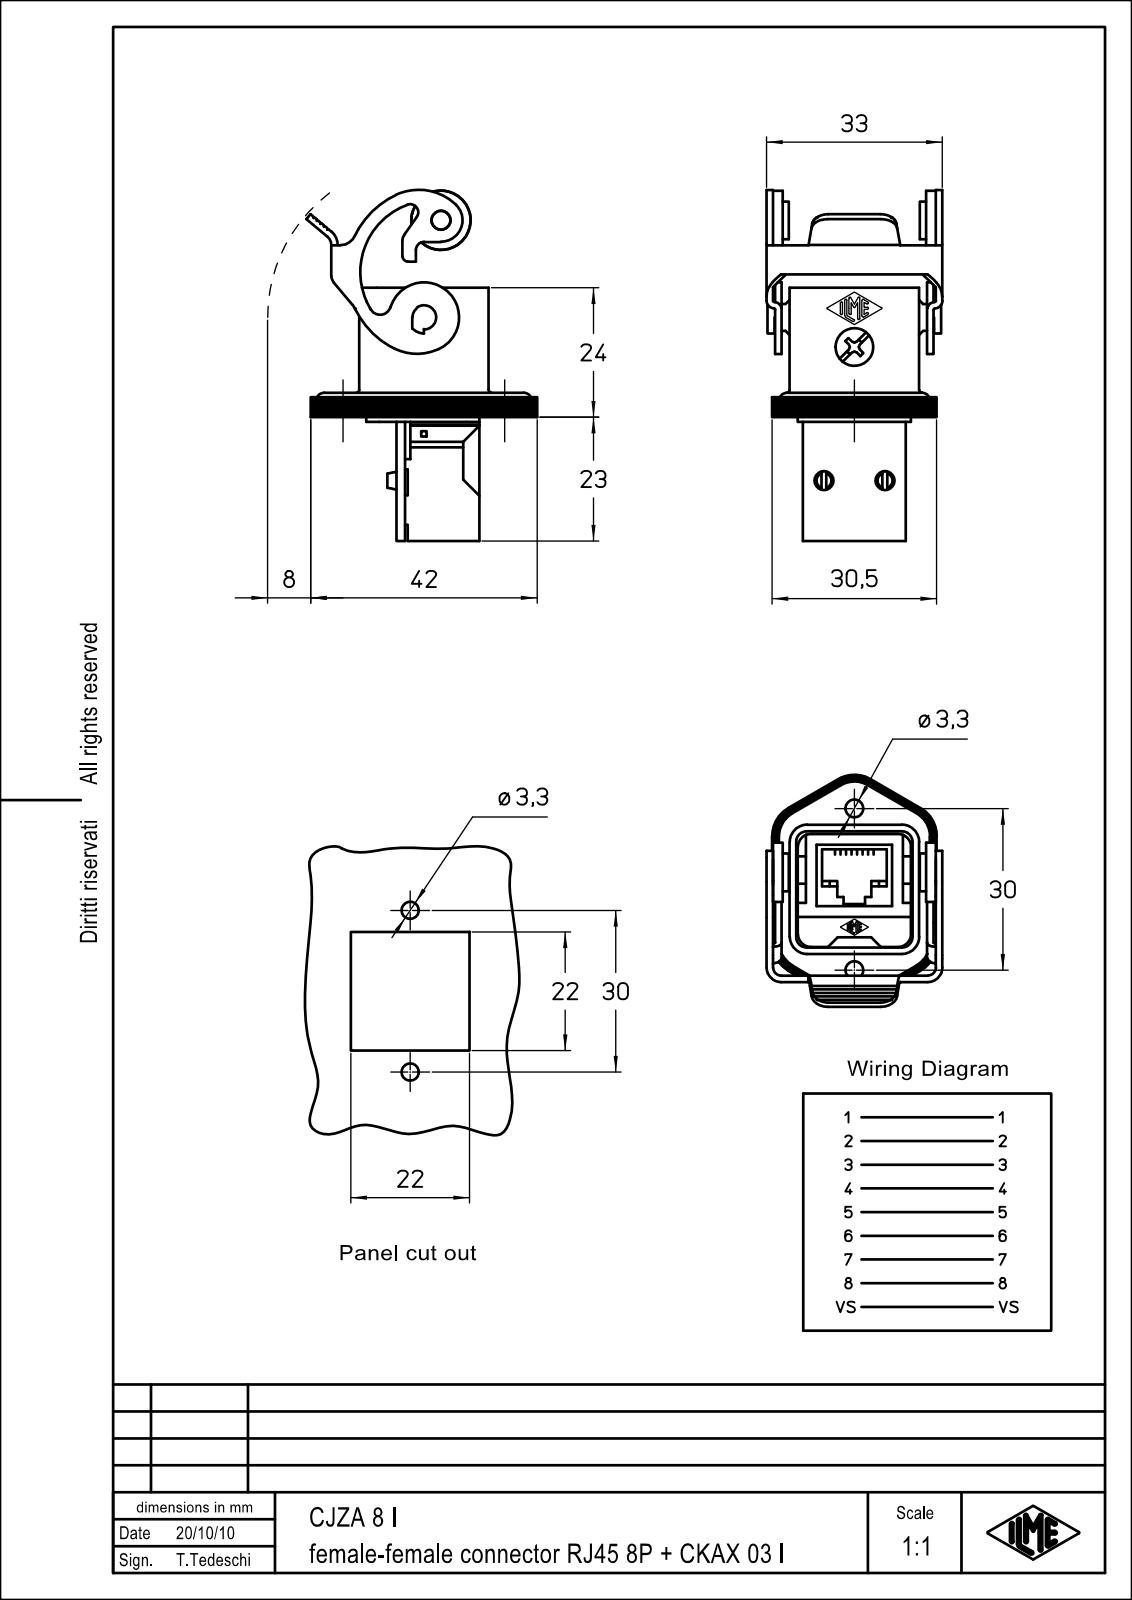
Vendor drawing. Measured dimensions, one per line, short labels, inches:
name: Cust_zama_I; CJZA_8_I
written by: Creo Elements/Direct Modeling 18.0B 02-Dec-2011 (C) Parametric Technology GmbH (AUTOMOTIVE_DESIGN)
unit: in
bodies: 1 solid, 577 faces (367 planar, 173 cylindrical, 37 other)
size: 2.573 × 1.695 × 1.299
volume: 1.081 in³; area: 23.42 in²
holes: 4× ⌀0.138, 2× ⌀0.13, 1× ⌀0.079, 1× ⌀0.197, 1× ⌀0.236
bosses: 4× ⌀0.134, 1× ⌀0.433, 1× ⌀0.276, 1× ⌀0.22, 1× ⌀0.197, 1× ⌀0.189, 1× ⌀0.169, 1× ⌀0.138
rounds: 16× R0.008, 14× R0.004, 8× R0.059, 8× R0.079, 6× R0.246, 5× R0.118, 5× R0.126, 4× R0.019
face distances: 0.063, 0.878, 0.047, 0.945, 0.157, 0.118, 0.606, 0.543, 0.787, 1.173
hole spacings: 0.266, 0.445, 0.839, 0.949, 1.009, 1.181
